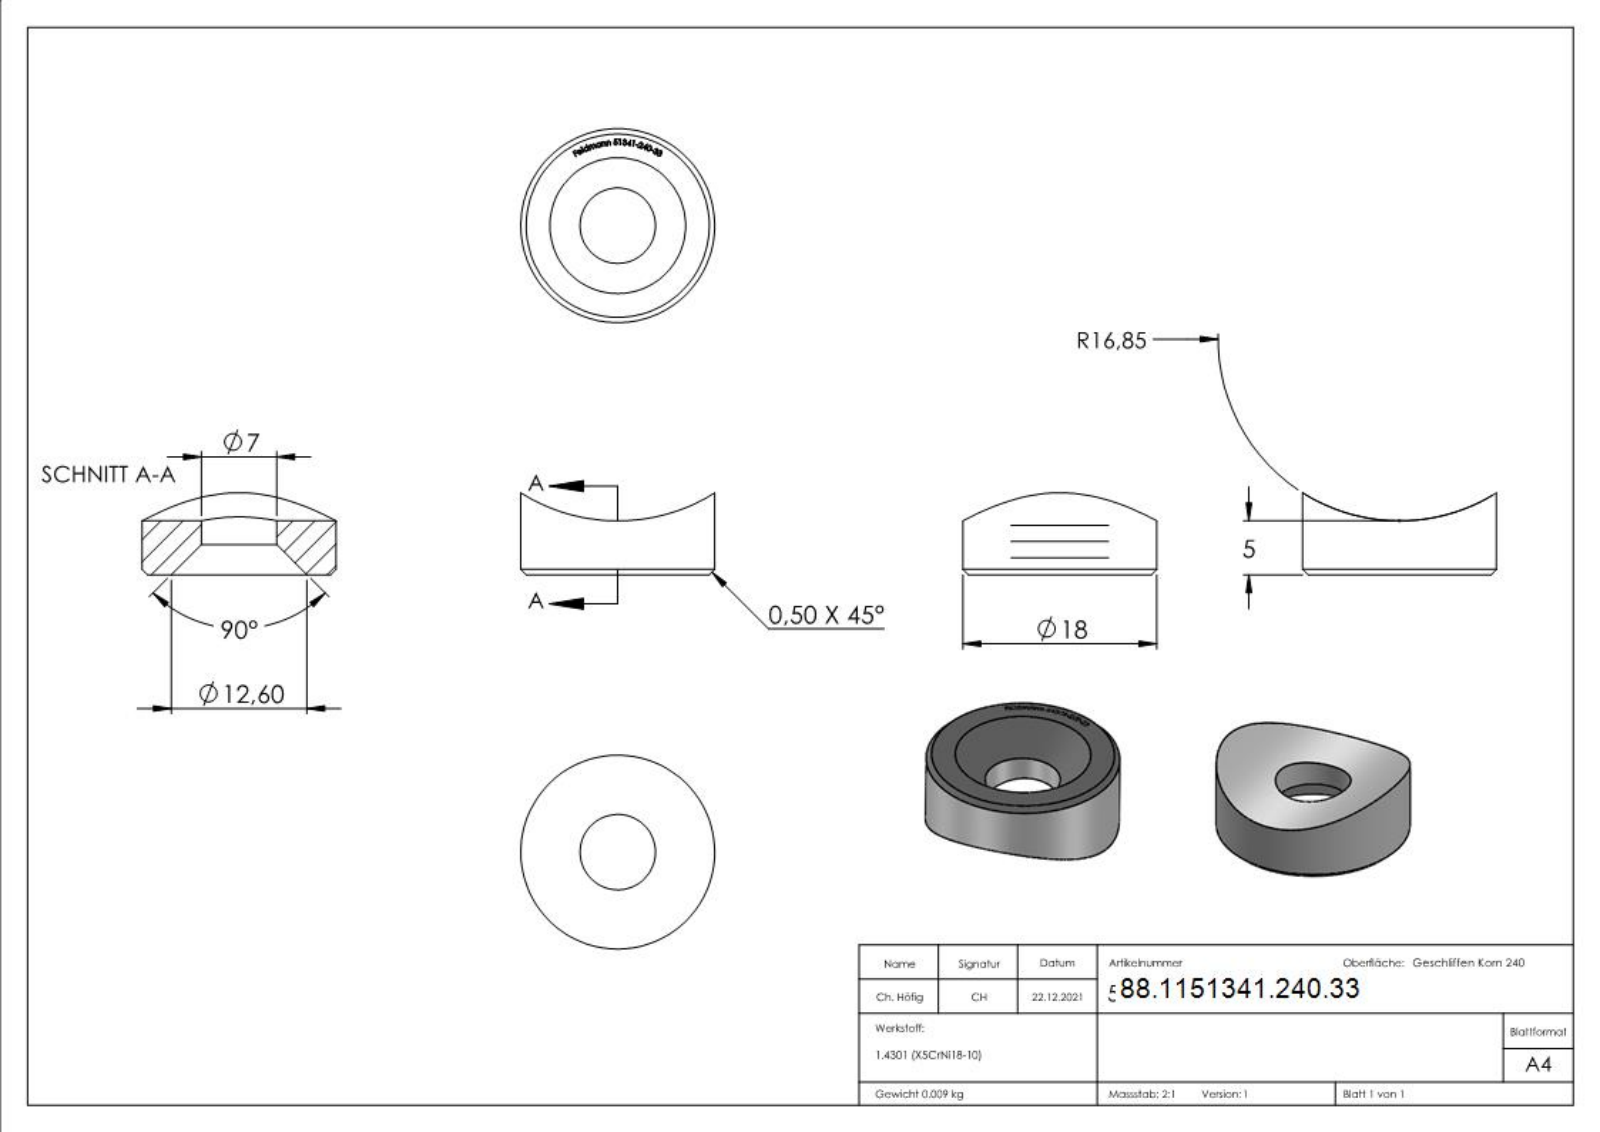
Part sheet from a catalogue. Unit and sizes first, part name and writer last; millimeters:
Units: millimetres
Overall size (bounding box): 18 × 18 × 7.61
Round holes (diameter × count): ⌀7 ×1
Round bosses / shafts (diameter × count): ⌀18 ×1
Partial cylindrical surfaces — rounded edges, fillets, slot ends (radius × count): R16.85 ×1
Main face-to-face distances: 0.5, 0.34, 0.32, 0.39, 0.53, 0.48, 0.54, 0.35, 0.38, 0.42
Volume: 1 119 mm³ · Surface area: 889 mm²
Bodies: 1 solid, 270 faces (148 planar, 5 cylindrical, 117 other)
Part name (STEP PRODUCT): 51341-240-33
STEP written by: SolidWorks 2018 (CONFIG_CONTROL_DESIGN)
